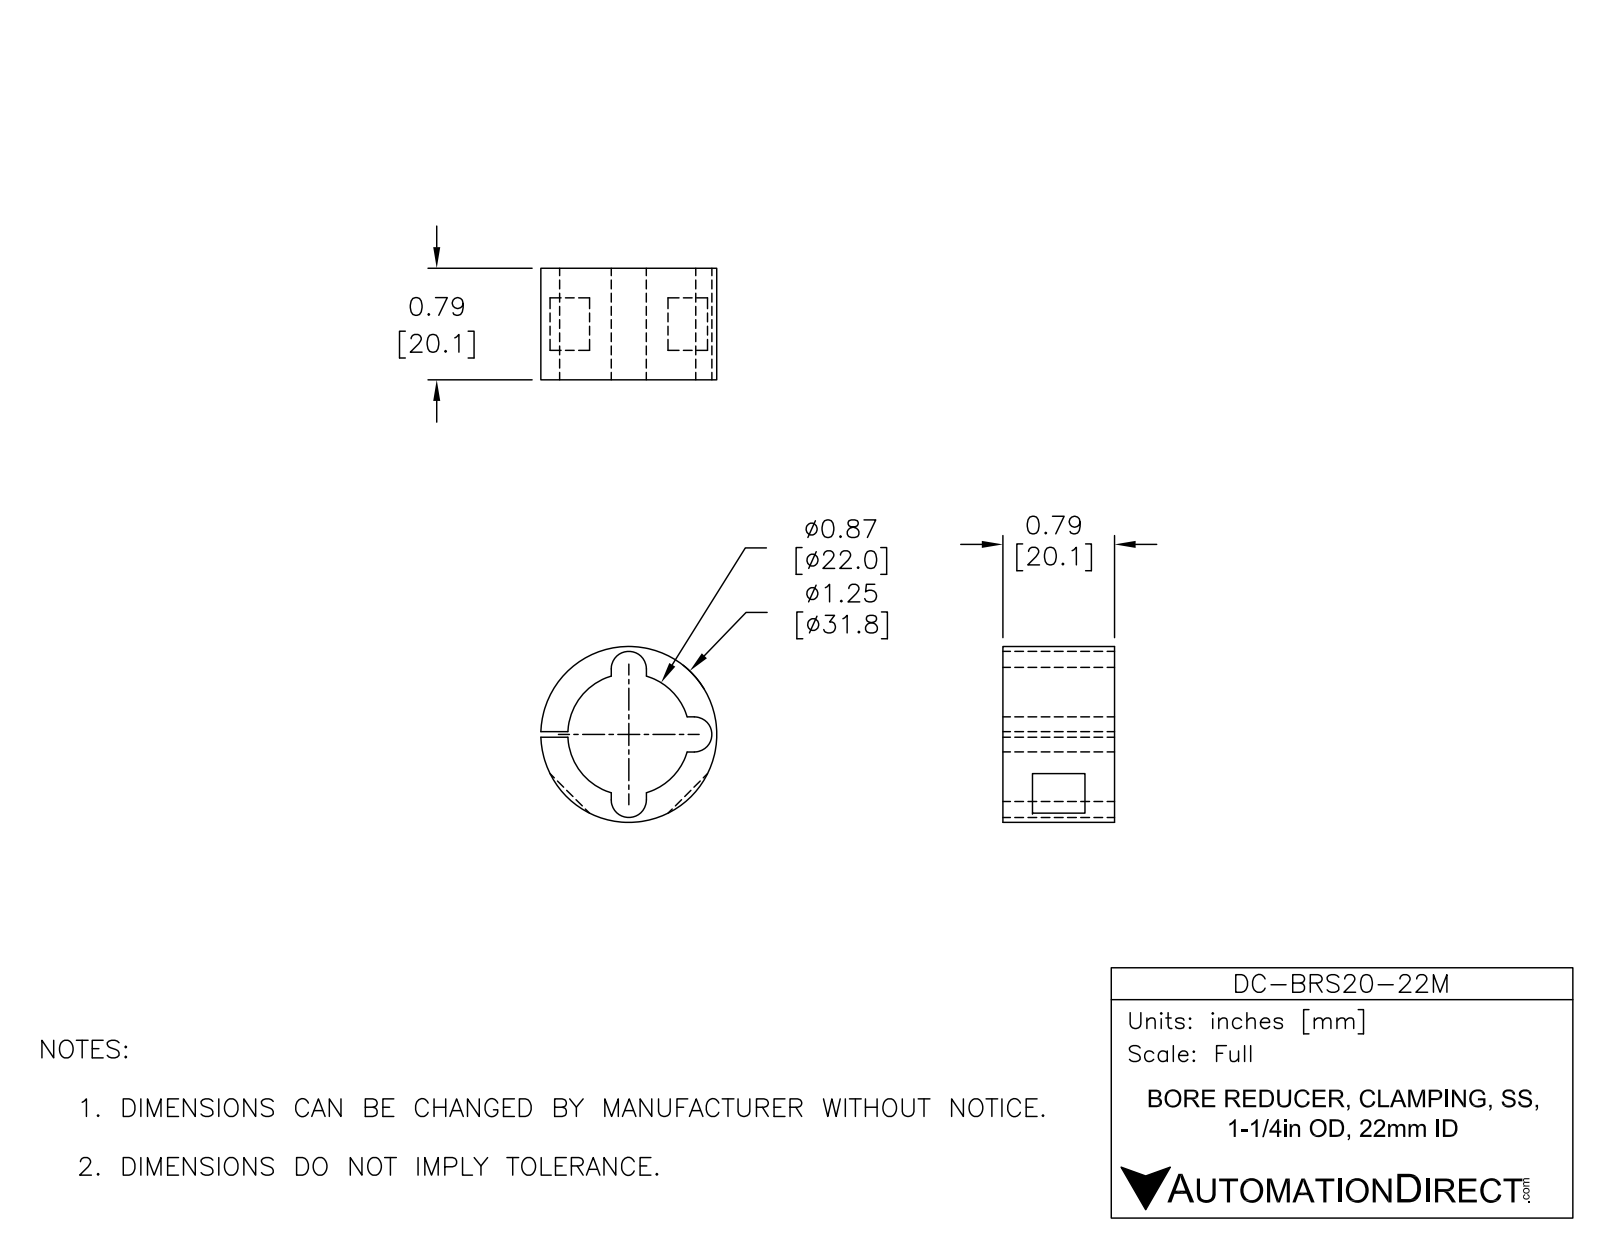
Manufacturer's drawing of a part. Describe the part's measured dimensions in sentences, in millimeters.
The part is named "DC-BRS20-22M". Its 3-D file was written by "SolidWorks 2015 (AUTOMOTIVE_DESIGN)". It is 1 solid with 27 faces: 16 planar, 11 cylindrical and 0 other. Overall it measures 31.75 by 31.74 by 20.14 millimeters. Its volume is 5 712 cubic millimeters and its surface area 4 483 square millimeters. Round bosses or shafts: 1 of diameter 31.75. Partial cylindrical surfaces (rounded edges, fillets, slot ends): 3 of radius 3.17, 1 of radius 12. The main face-to-face distances are 20.14, 1.02, 5.33, 14.81, 9.48, 2.66, 3.68, 6.34, 6.35.
